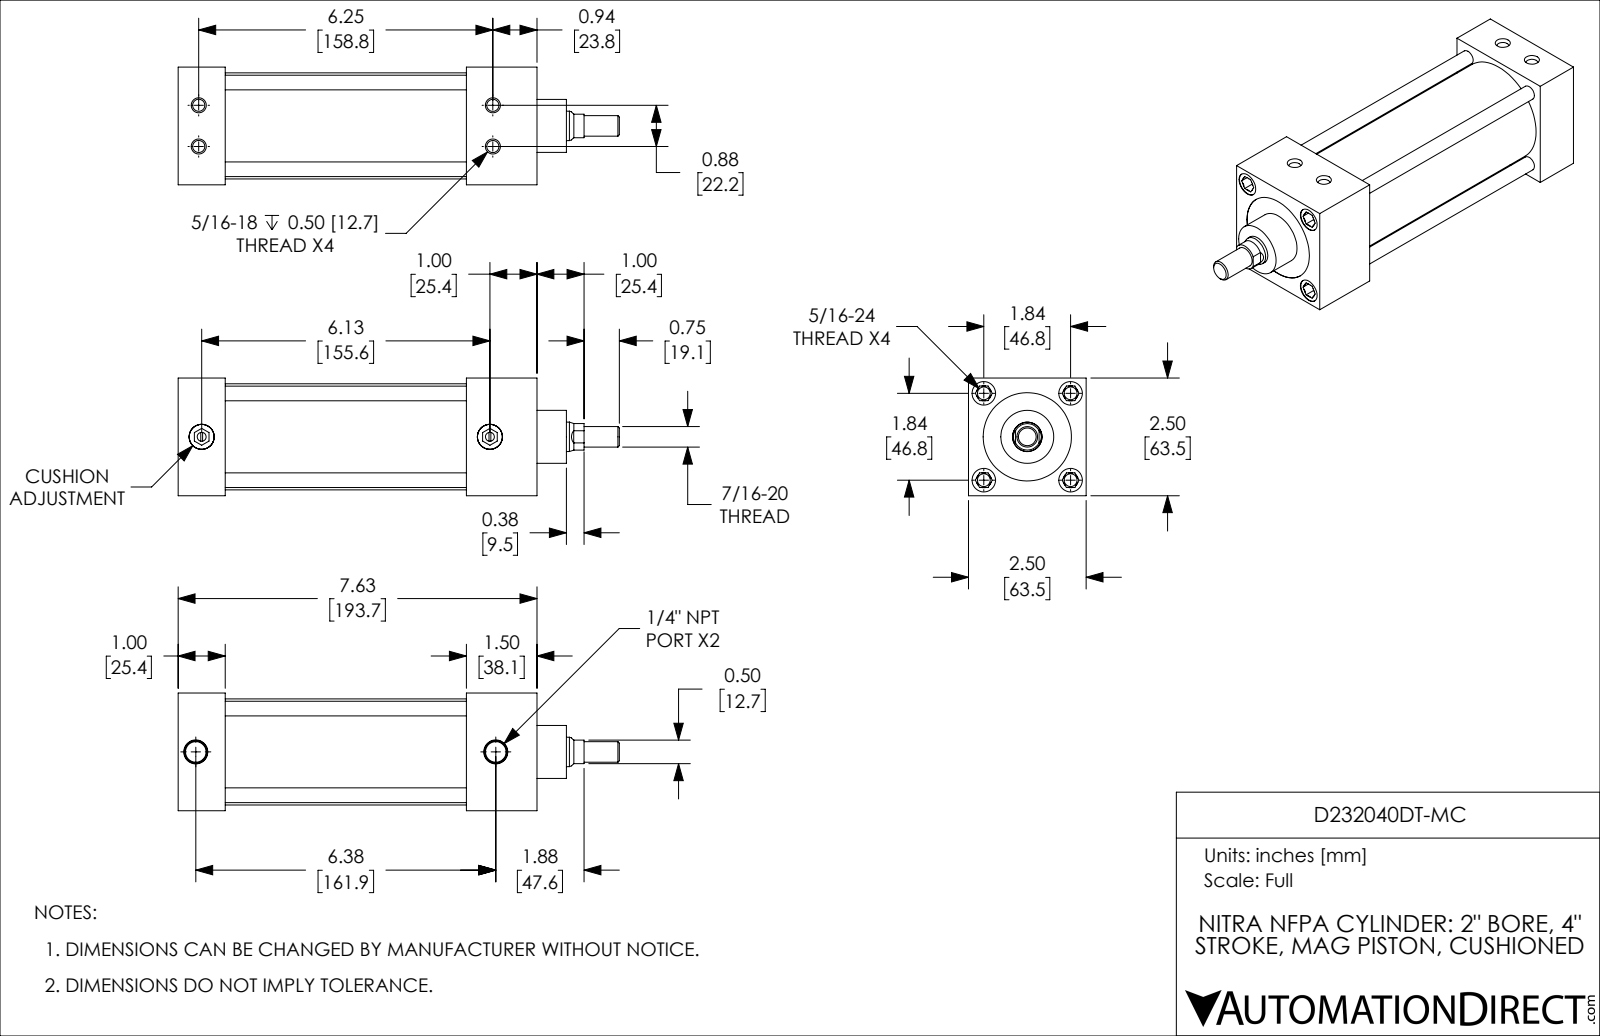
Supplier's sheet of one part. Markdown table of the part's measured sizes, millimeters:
| quantity | value |
| --- | --- |
| part name | D232040DT-MC_CUSHION; D232040DT-MC; D232040DT-MC_BODY; D232040DT-MC_PISTON_KK1 |
| STEP written by | SolidWorks 2019 (CONFIG_CONTROL_DESIGN) |
| units | millimeters |
| bodies | 4 solids, 248 faces (90 planar, 78 cylindrical, 80 other) |
| overall size | 238.1 × 63.5 × 63.5 |
| volume | 429 500 mm³ |
| surface area | 116 700 mm² |
| round holes (diameter × count) | 6.9 × 7, 6.5 × 4, 12.7 × 4, 4.8 × 2, 11.1 × 2, 13.5 × 2, 15.9 × 1, 47.6 × 1, 50.8 × 1 |
| round bosses / shafts (diameter × count) | 7.9 × 4, 13.5 × 2, 57.2 × 1, 50.8 × 1, 28.6 × 1, 15.8 × 1, 11.1 × 1 |
| partial cylindrical surfaces (radius × count) | 7.1 × 1 |
| main face-to-face distances | 63.5, 25.4, 155.6, 130.2, 28.6, 54, 101.6, 38.1, 193.7, 168.3 |
| hole center spacings | 46.7, 46.8, 33, 11.2, 11.3, 22.2, 33.1, 66.1 |
